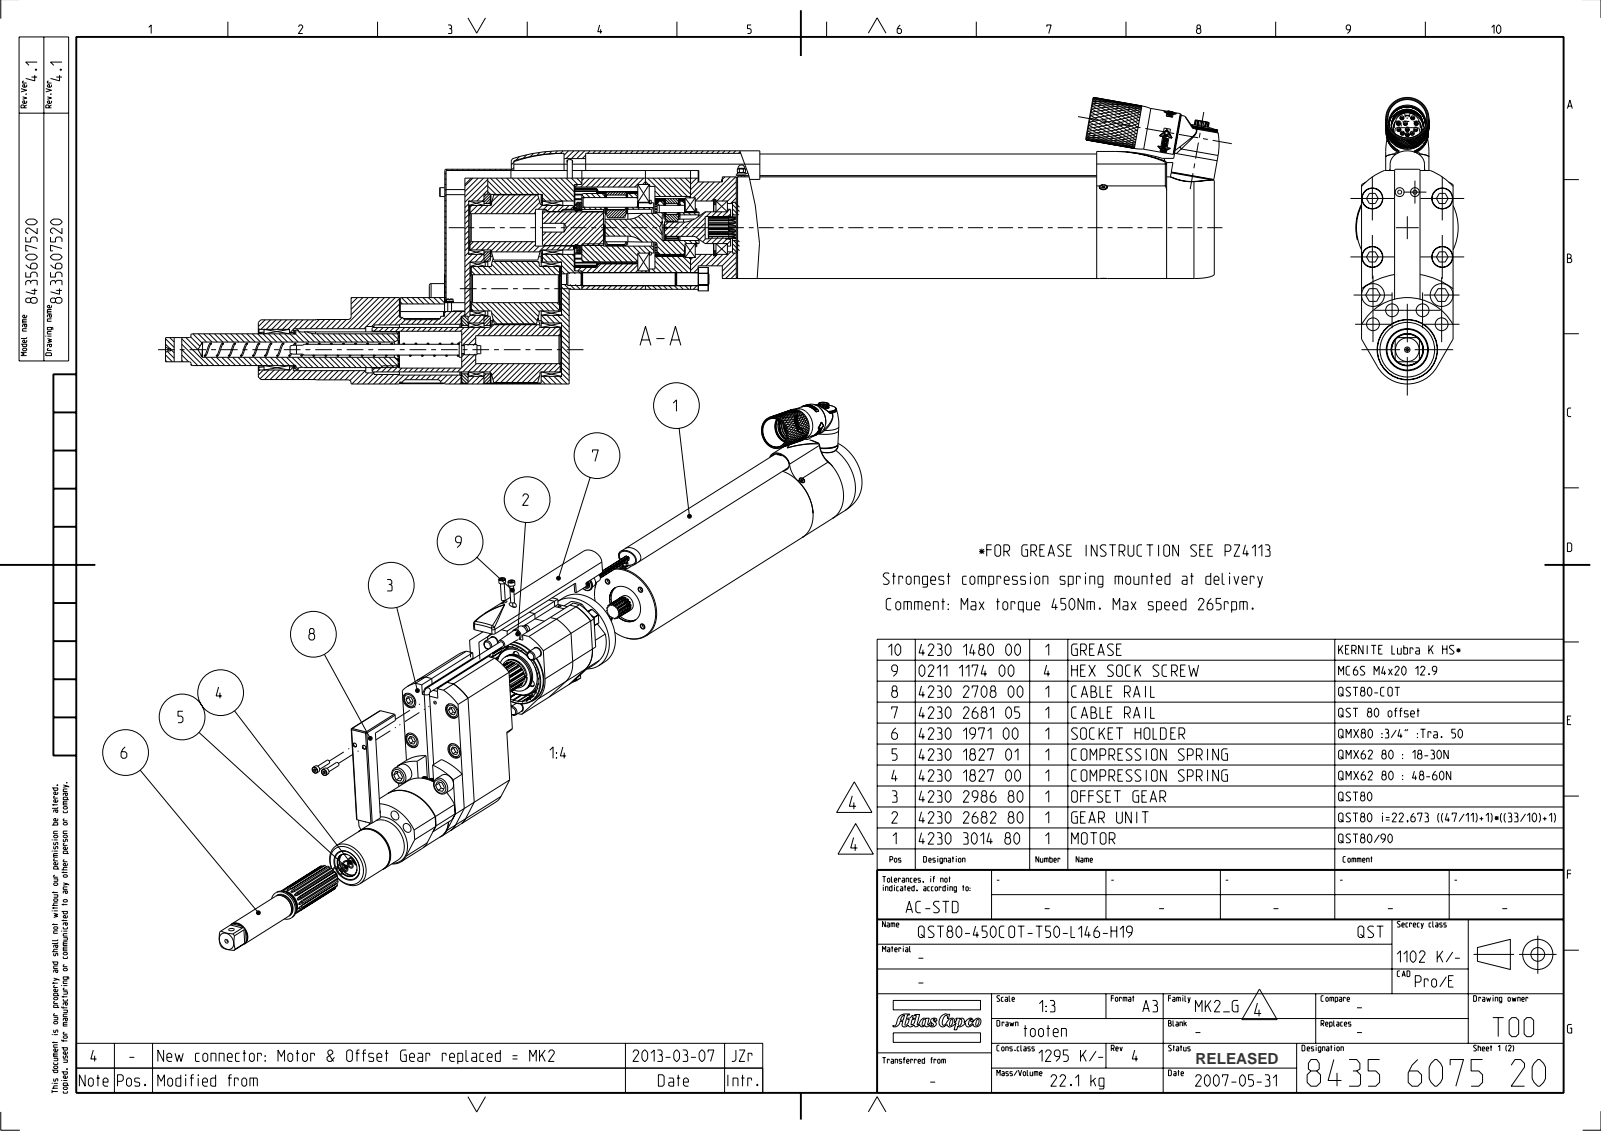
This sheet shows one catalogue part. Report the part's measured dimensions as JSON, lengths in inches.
{"part_name": "8435607520_SW0001", "step_written_by": "CREO PARAMETRIC BY PTC INC, 2022414 (CONFIG_CONTROL_DESIGN)", "units": "inches", "bodies": {"solids": 9, "faces": 3095, "planar": 1929, "cylindrical": 535, "other": 631}, "overall_size": [32.629, 8.879, 3.169], "volume_in3": 254.6, "surface_area_in2": 549.6, "round_holes": [[0.02, 8], [0.177, 4], [0.398, 4], [0.406, 4], [0.65, 4], [0.128, 2], [0.295, 2], [0.33, 2], [0.413, 2], [0.693, 2], [0.079, 1], [0.126, 1]], "round_bosses_or_shafts": [[0.055, 8], [0.039, 8], [0.02, 8], [0.217, 7], [0.63, 6], [0.394, 5], [0.276, 4], [0.157, 4]], "partial_cylinders_radius": [[0.008, 54], [0.02, 12], [0.039, 7], [0.128, 5], [0.031, 4], [0.047, 4], [0.118, 4], [0.012, 2]], "face_to_face_distances": [2.835, 0.039, 1.024, 1.811, 0.748, 3.228, 19.98, 23.209, 1.063, 1.772], "hole_center_spacings": [0.079, 0.154, 0.123, 0.068, 1.582, 0.069, 0.472, 2.087]}
